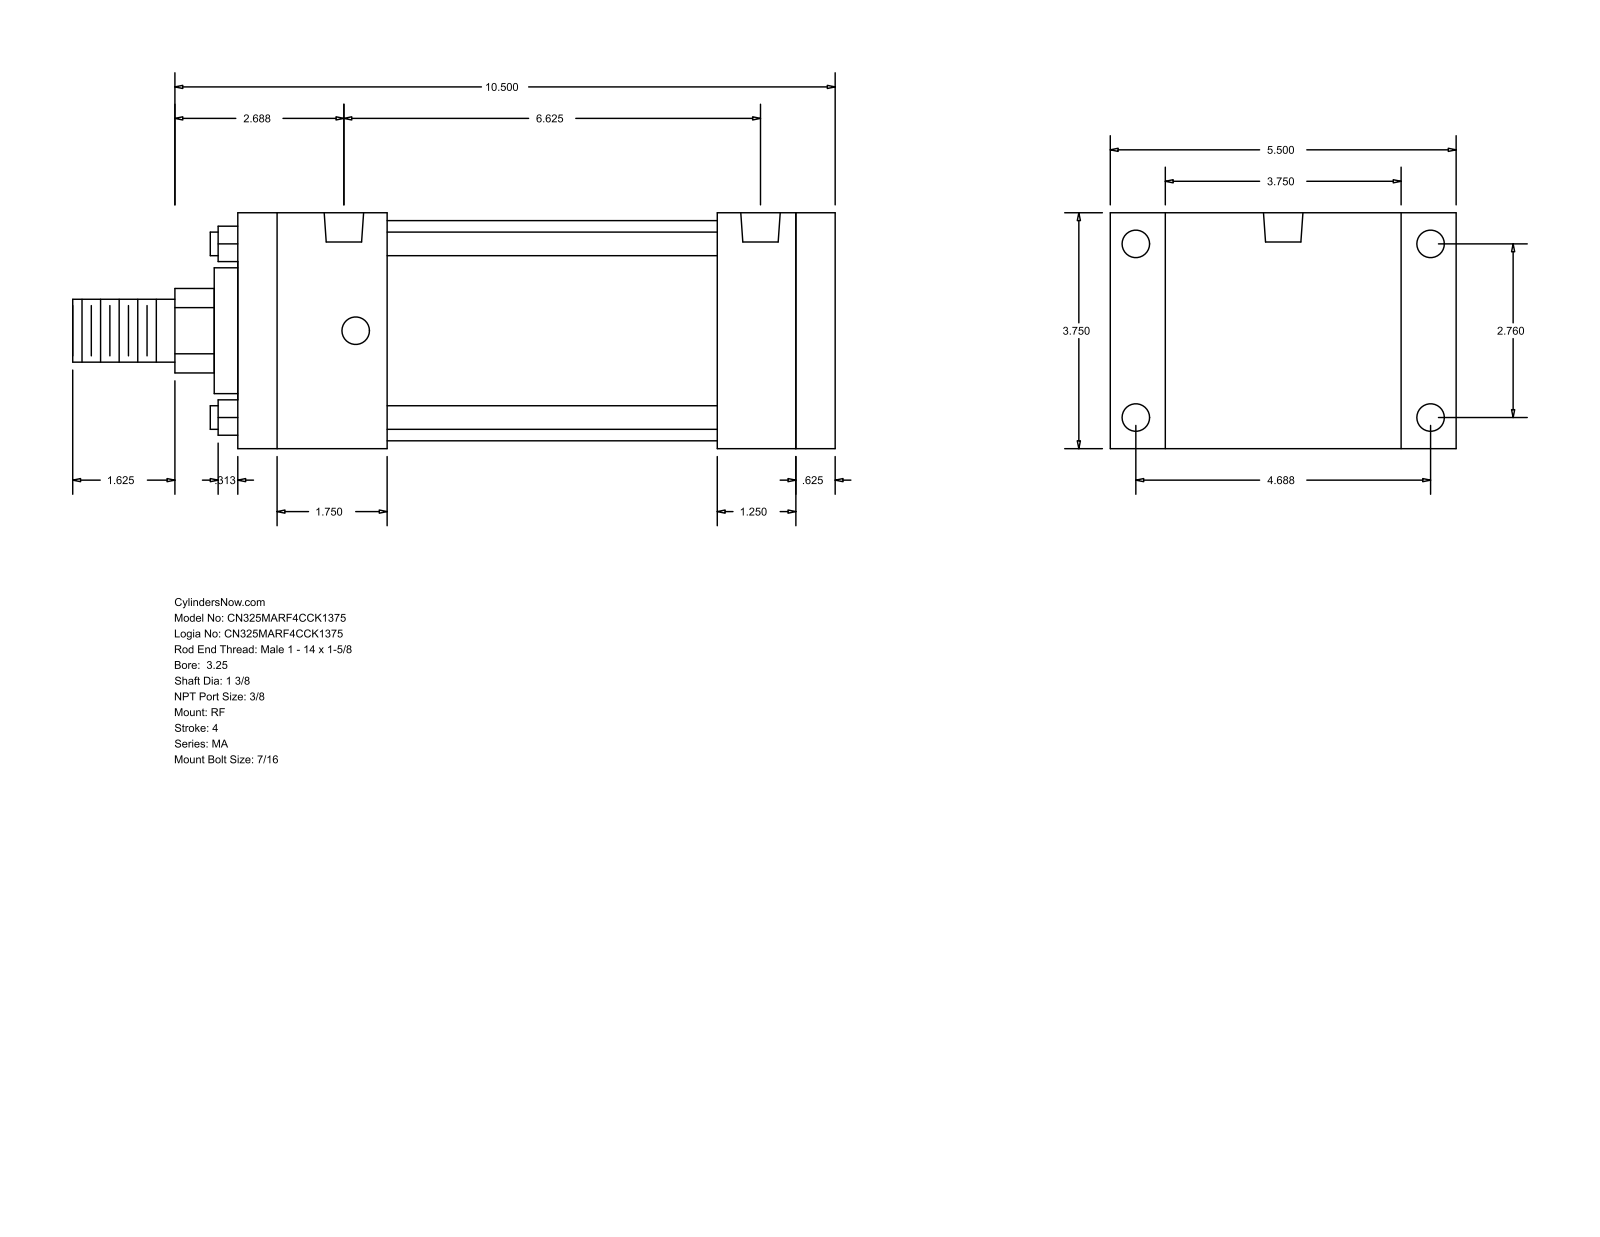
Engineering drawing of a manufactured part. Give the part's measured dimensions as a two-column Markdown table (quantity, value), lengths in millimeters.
| quantity | value |
| --- | --- |
| part name | MA_RF__0325_1.375 |
| STEP written by | GSSL Pune (CONFIG_CONTROL_DESIGN) |
| units | millimeters |
| bodies | 0 solids, 92 faces (64 planar, 28 cylindrical, 0 other) |
| overall size | 307.98 × 139.7 × 95.25 |
| round holes (diameter × count) | 11.11 × 8, 15.93 × 2 |
| round bosses / shafts (diameter × count) | 9.53 × 4, 88.9 × 1, 50.8 × 1, 34.92 × 1, 25.4 × 1 |
| partial cylindrical surfaces (radius × count) | 17.06 × 1 |
| main face-to-face distances | 95.24, 241.3, 15.88, 225.42, 22.23, 117.47, 193.67, 31.75, 47.63, 60.32 |
| hole center spacings | 70.1, 119.06, 138.16, 158.75, 4.76, 4.77, 163.51, 163.52 |
